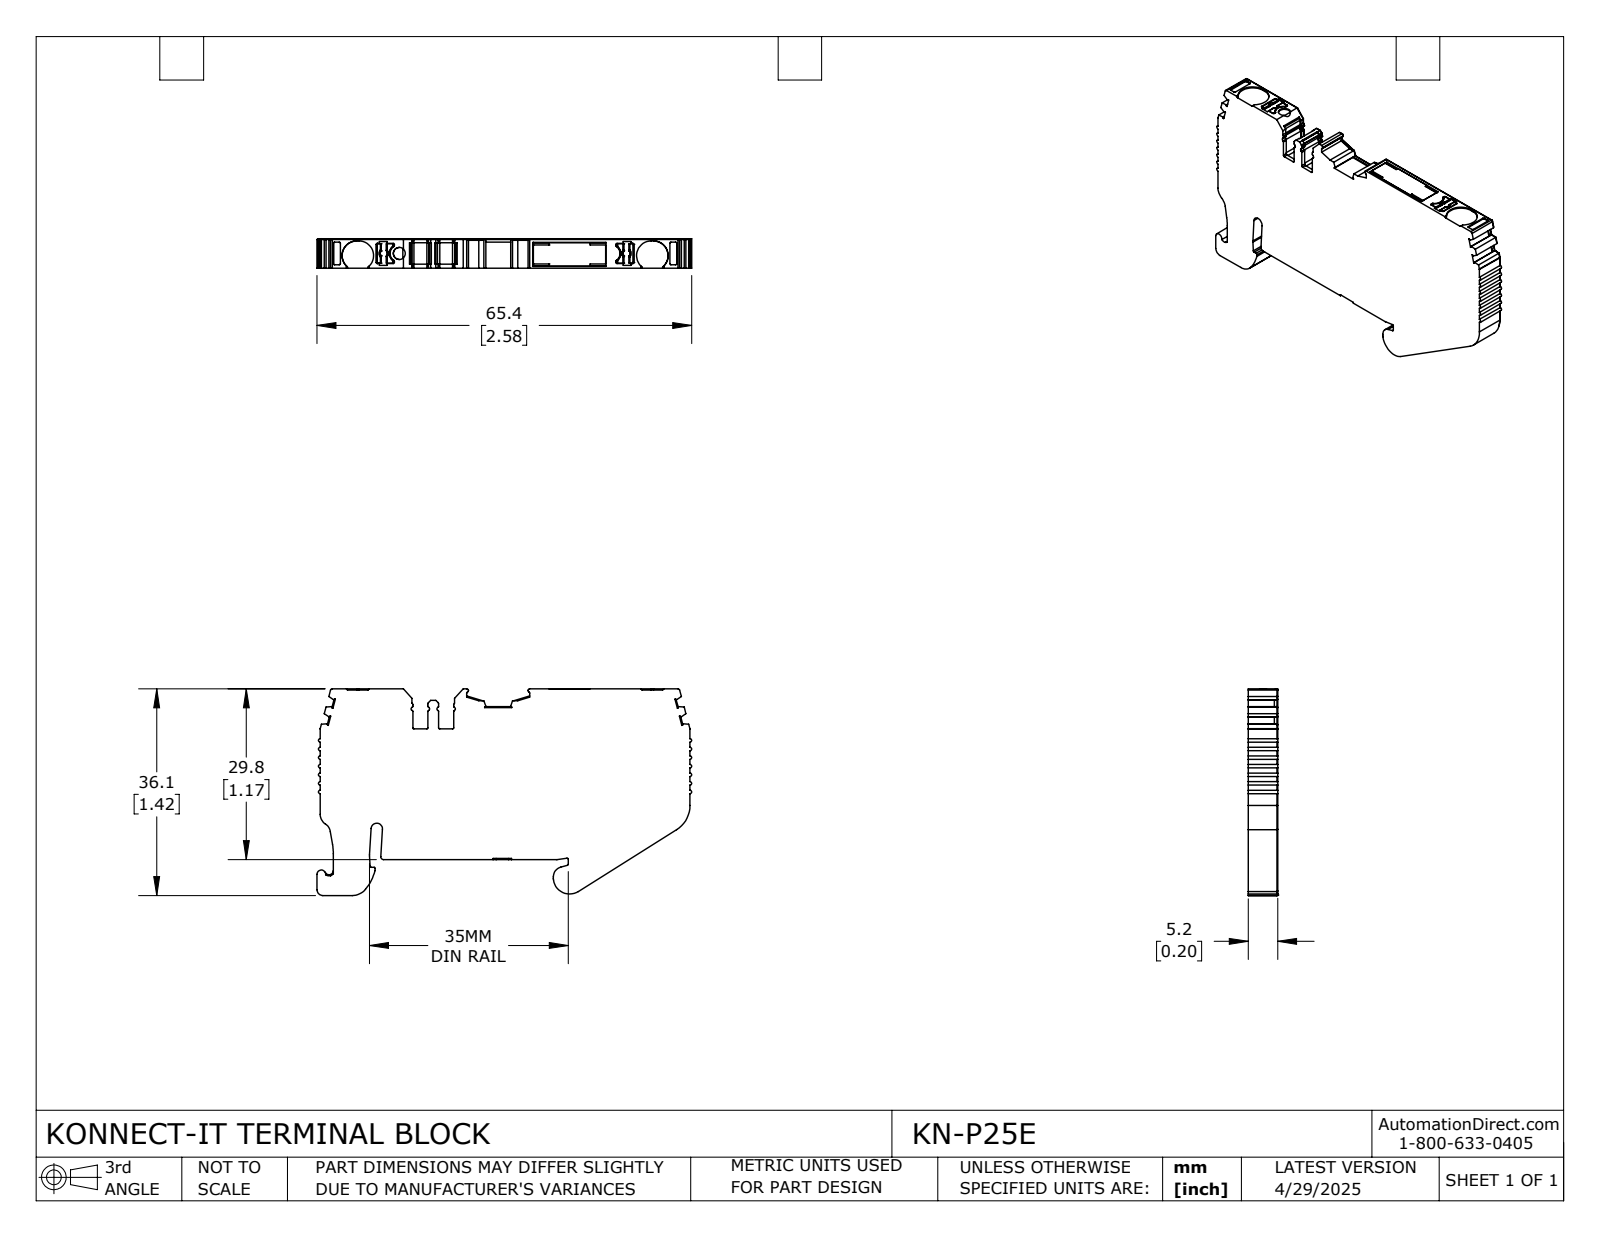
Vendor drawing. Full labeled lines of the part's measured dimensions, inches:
Part name (STEP PRODUCT): KN-P25E
STEP written by: SolidWorks 2024 (CONFIG_CONTROL_DESIGN)
Units: inches
Bodies: 1 solid, 607 faces (340 planar, 230 cylindrical, 37 other)
Overall size (bounding box): 2.576 × 1.42 × 0.203
Volume: 0.585 in³ · Surface area: 7.972 in²
Round holes (diameter × count): ⌀0.083 ×1
Partial cylindrical surfaces — rounded edges, fillets, slot ends (radius × count): R0.008 ×54, R0.012 ×39, R0.02 ×18, R0.004 ×17, R0.016 ×9, R0.006 ×8, R0.1 ×4, R0.039 ×3
Main face-to-face distances: 0.203, 1.174, 1.166, 2.543, 0.177, 0.197, 0.246, 1.412, 0.079, 1.42
